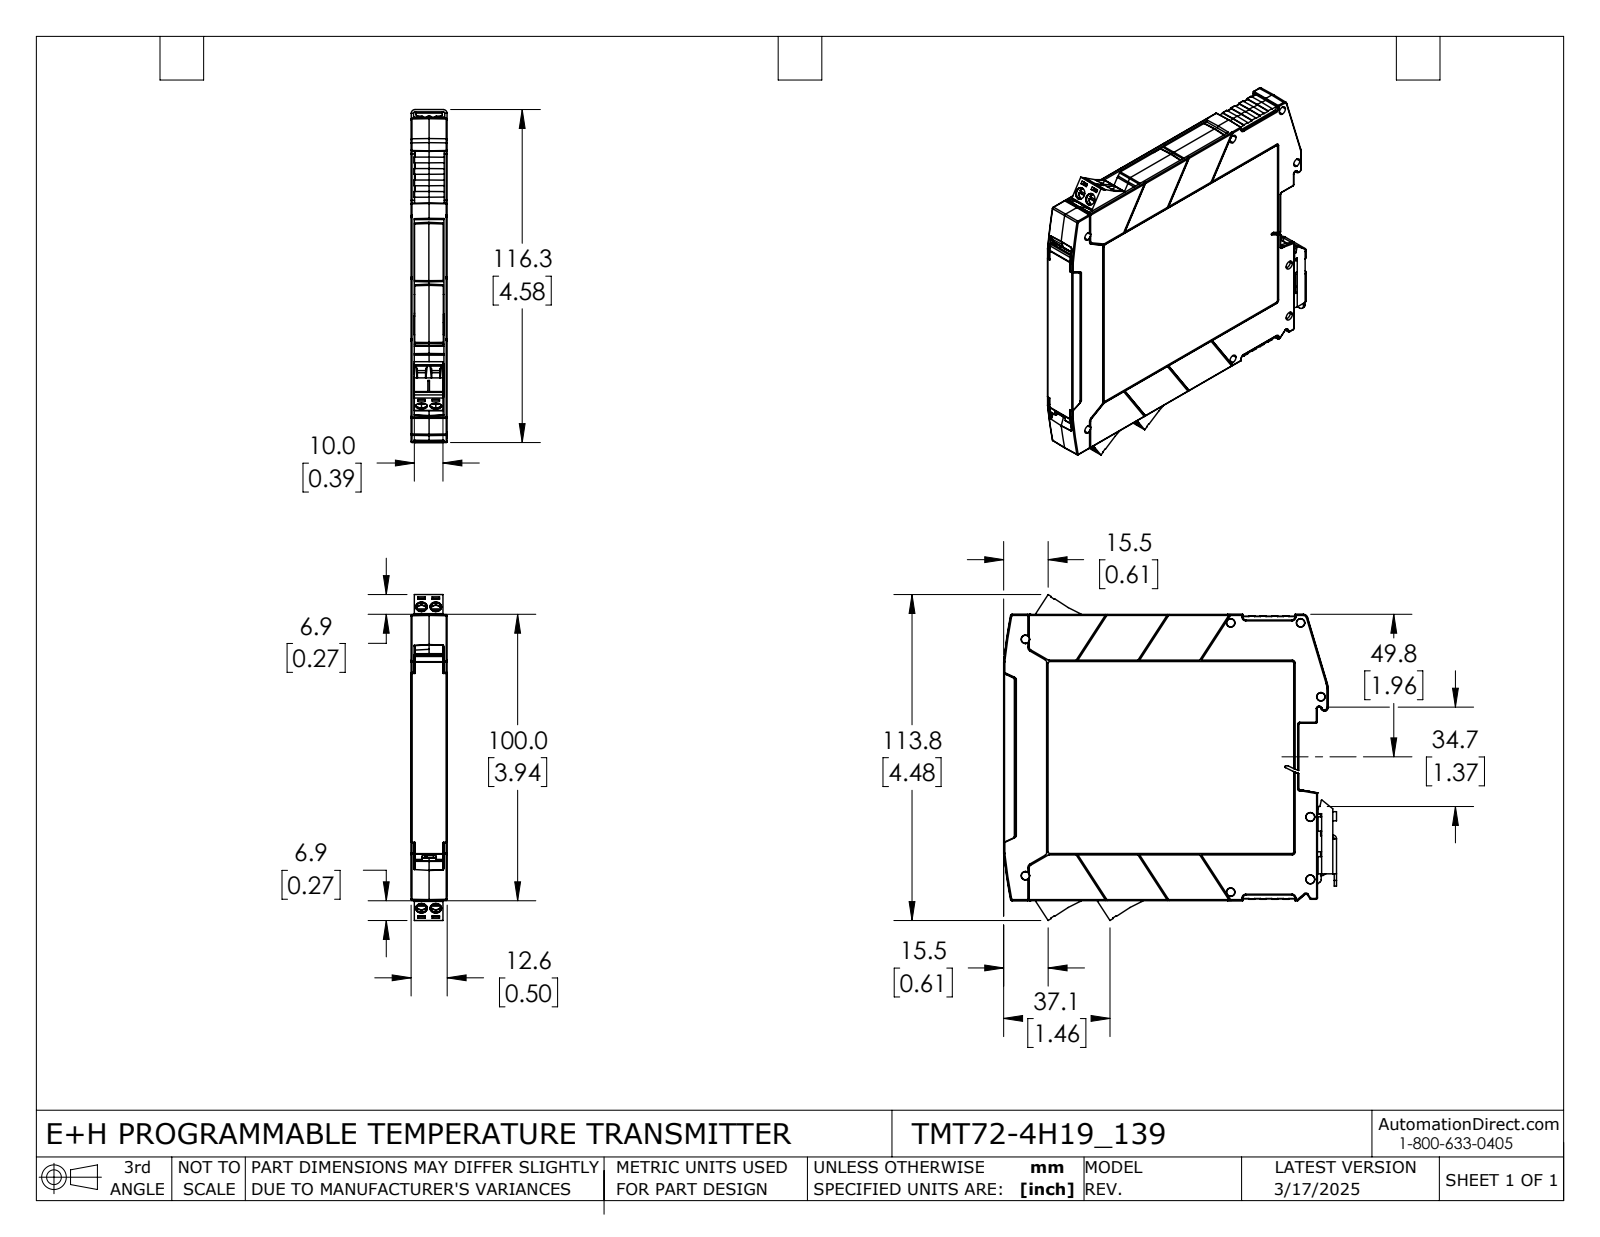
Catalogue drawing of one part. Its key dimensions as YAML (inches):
part_name: "TMT72-4H19_139"
step_written_by: "SolidWorks 2024 (AUTOMOTIVE_DESIGN)"
units: inches
bodies: {solids: 1, faces: 2495, planar: 1056, cylindrical: 820, other: 619}
overall_size: [4.577, 4.43, 0.571]
volume: 8.693
surface_area: 51.78
round_holes:
  - {diameter: 0.118, count: 2}
  - {diameter: 0.111, count: 1}
  - {diameter: 0.121, count: 1}
  - {diameter: 0.183, count: 1}
partial_cylinders:
  - {radius: 0.008, count: 252}
  - {radius: 0.02, count: 71}
  - {radius: 0.012, count: 63}
  - {radius: 0.031, count: 34}
  - {radius: 0.039, count: 22}
  - {radius: 0.011, count: 15}
  - {radius: 0.016, count: 10}
  - {radius: 0.079, count: 9}
face_to_face_distances: [0.031, 0.047, 0.127, 0.174, 3.906, 0.039, 0.059, 0.075, 3.831, 0.028]
hole_center_spacings: [1.108, 2.514, 2.832, 2.957, 3.918, 4.75]
